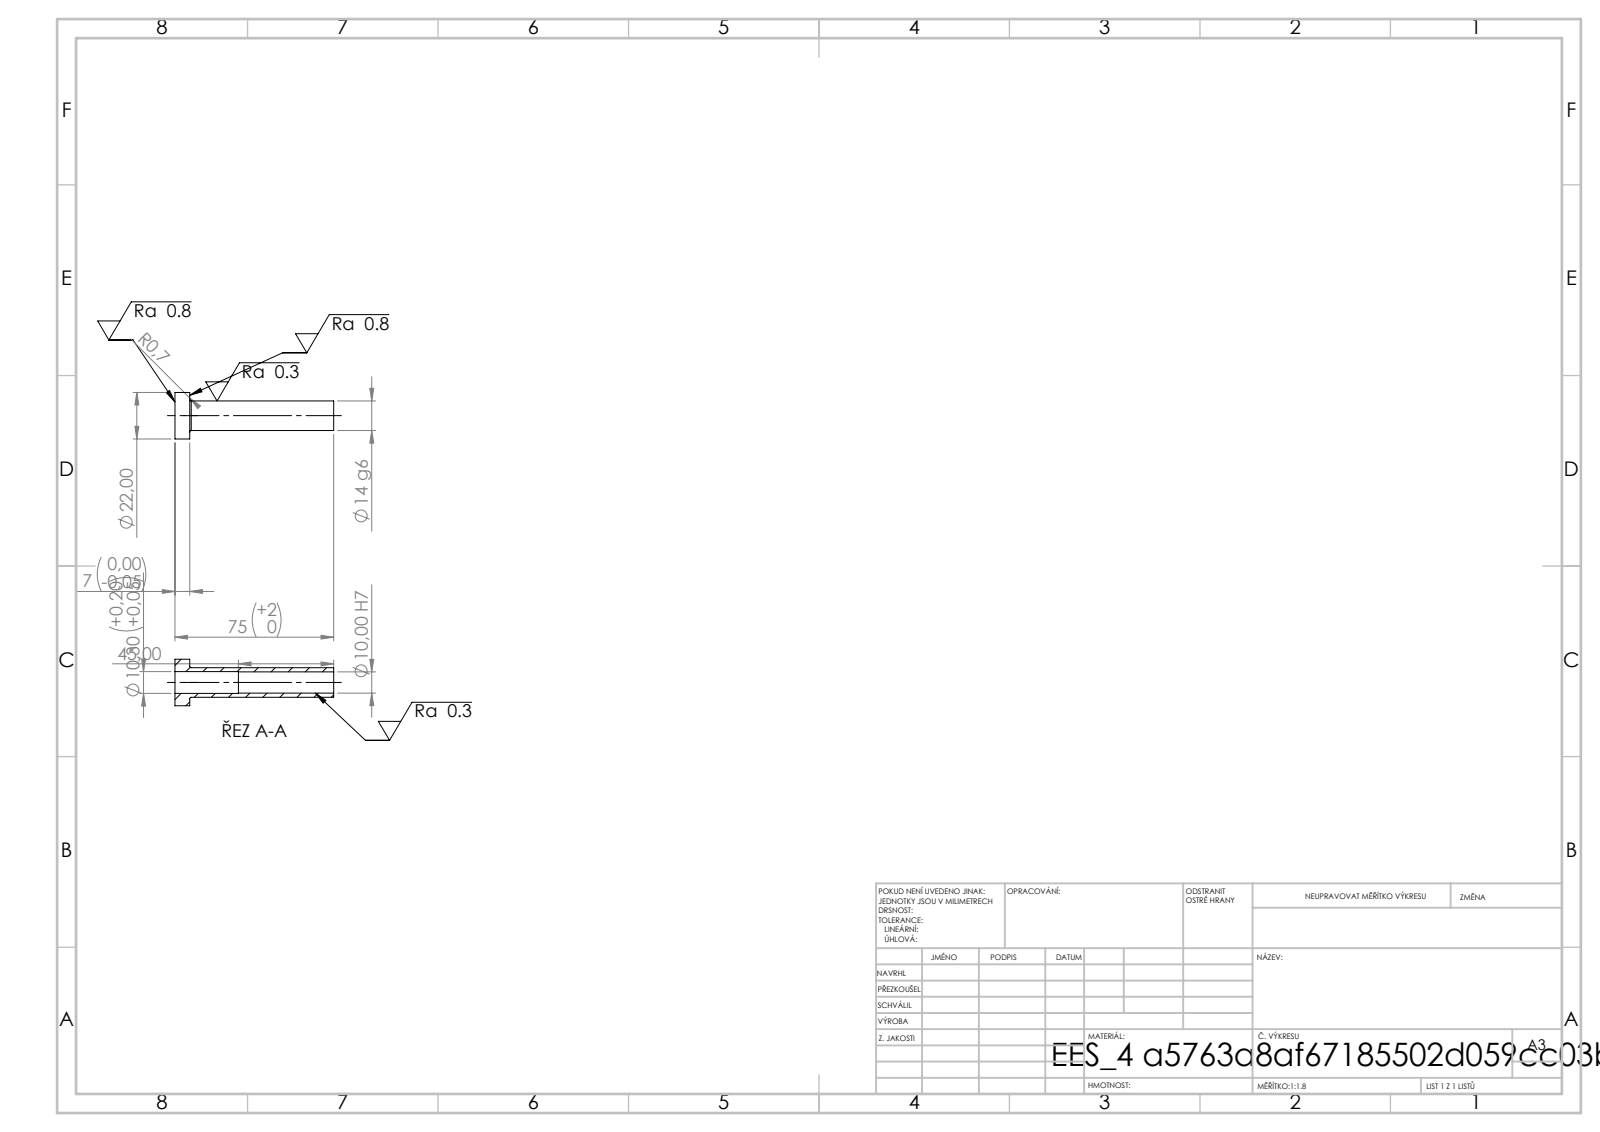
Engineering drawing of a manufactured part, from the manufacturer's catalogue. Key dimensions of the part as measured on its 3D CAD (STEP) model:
STEP written by: SolidWorks 2019 (CONFIG_CONTROL_DESIGN)
Units: millimetres
Bodies: 1 solid, 14 faces (4 planar, 8 cylindrical, 2 other)
Overall size (bounding box): 75 × 22 × 22
Volume: 7 099 mm³ · Surface area: 6 449 mm²
Round holes (diameter × count): ⌀10 ×1, ⌀10.3 ×1
Round bosses / shafts (diameter × count): ⌀22 ×1, ⌀14 ×1
Main face-to-face distances: 7, 75, 68, 30, 23, 45
